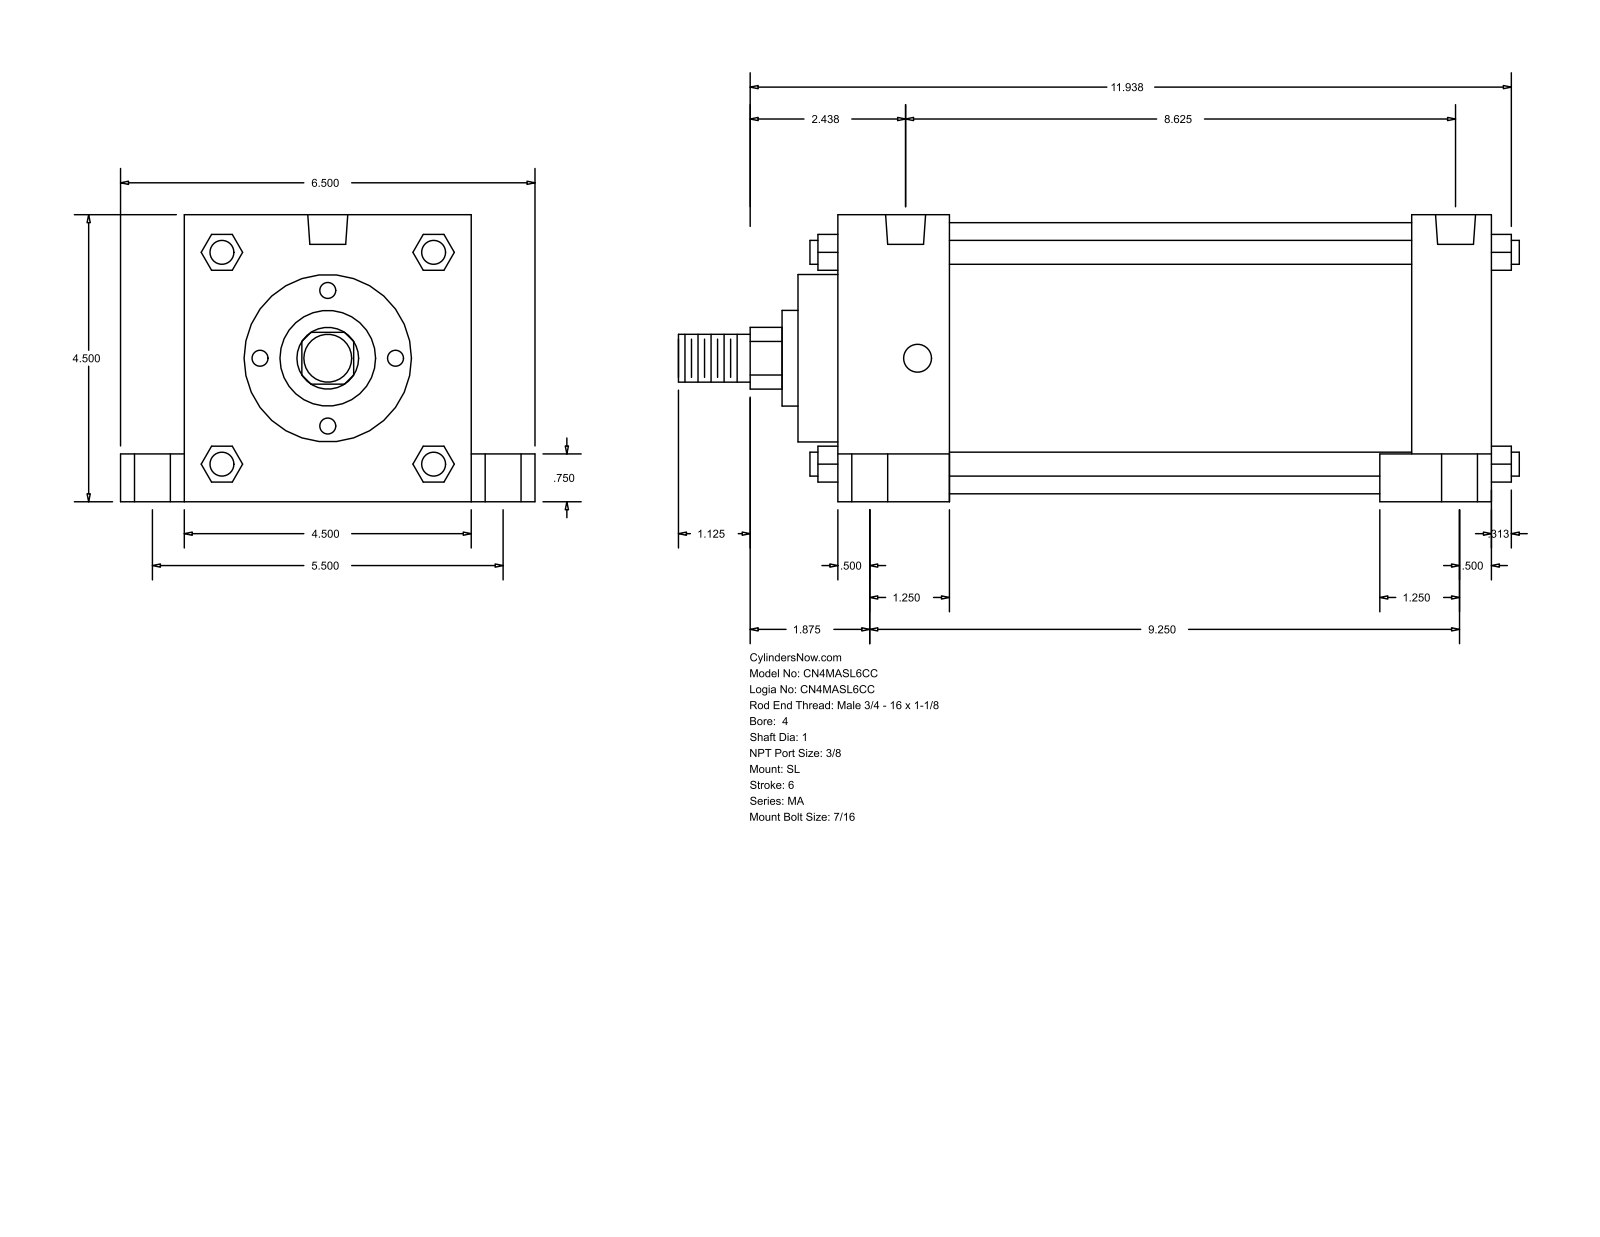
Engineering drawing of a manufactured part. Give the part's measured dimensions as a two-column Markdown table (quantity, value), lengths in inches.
| quantity | value |
| --- | --- |
| part name | MA_SL__0400_1 |
| STEP written by | GSSL Pune (CONFIG_CONTROL_DESIGN) |
| units | inches |
| bodies | 0 solids, 150 faces (113 planar, 37 cylindrical, 0 other) |
| overall size | 13.187 × 6.5 × 4.5 |
| round holes (diameter × count) | 0.437 × 4, 0.563 × 4, 0.813 × 4, 0.627 × 2 |
| round bosses / shafts (diameter × count) | 0.375 × 4, 4.25 × 1, 2.625 × 1, 1.5 × 1, 1 × 1, 0.75 × 1 |
| partial cylindrical surfaces (radius × count) | 0.484 × 1 |
| main face-to-face distances | 4.5, 10.25, 1.75, 8.5, 9, 7.25, 1.25, 1, 5.5, 10.875 |
| hole center spacings | 0.187, 2.751, 2.761, 2.807, 2.85, 5.5, 8.25, 8.438 |
